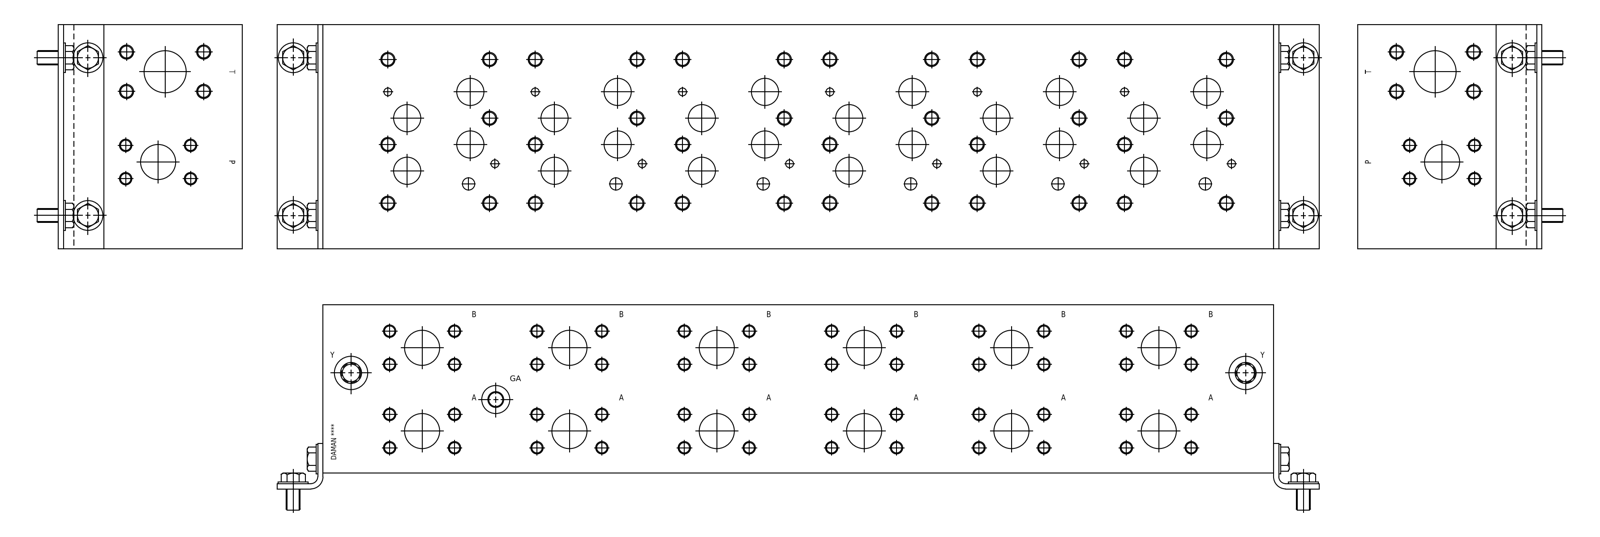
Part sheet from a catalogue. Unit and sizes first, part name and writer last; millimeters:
Units: millimetres
Overall size (bounding box): 860.42 × 203.2 × 152.4
Round holes (diameter × count): ⌀11.13 ×61, ⌀9.35 ×55, ⌀12.7 ×44, ⌀10.72 ×42, ⌀24.61 ×24, ⌀31.75 ×13, ⌀7.14 ×12, ⌀17.5 ×2, ⌀19.05 ×2, ⌀19.25 ×2, ⌀30.63 ×2, ⌀12.29 ×1
Main face-to-face distances: 152.4, 203.2, 860.42, 28.45, 30.23, 174.75, 122.17, 0.79, 27.66, 202.41
Hole centre spacings: 133.35, 266.7, 153.2, 136.72, 30.18, 66.02, 75.41, 95.58
Volume: 25 970 000 mm³ · Surface area: 841 166 mm²
Bodies: 1 solid, 1236 faces (568 planar, 281 cylindrical, 387 other)
Part name (STEP PRODUCT): Part_AD08HP065F_3D
STEP written by: Autodesk Inventor 2021 (AUTOMOTIVE_DESIGN)
